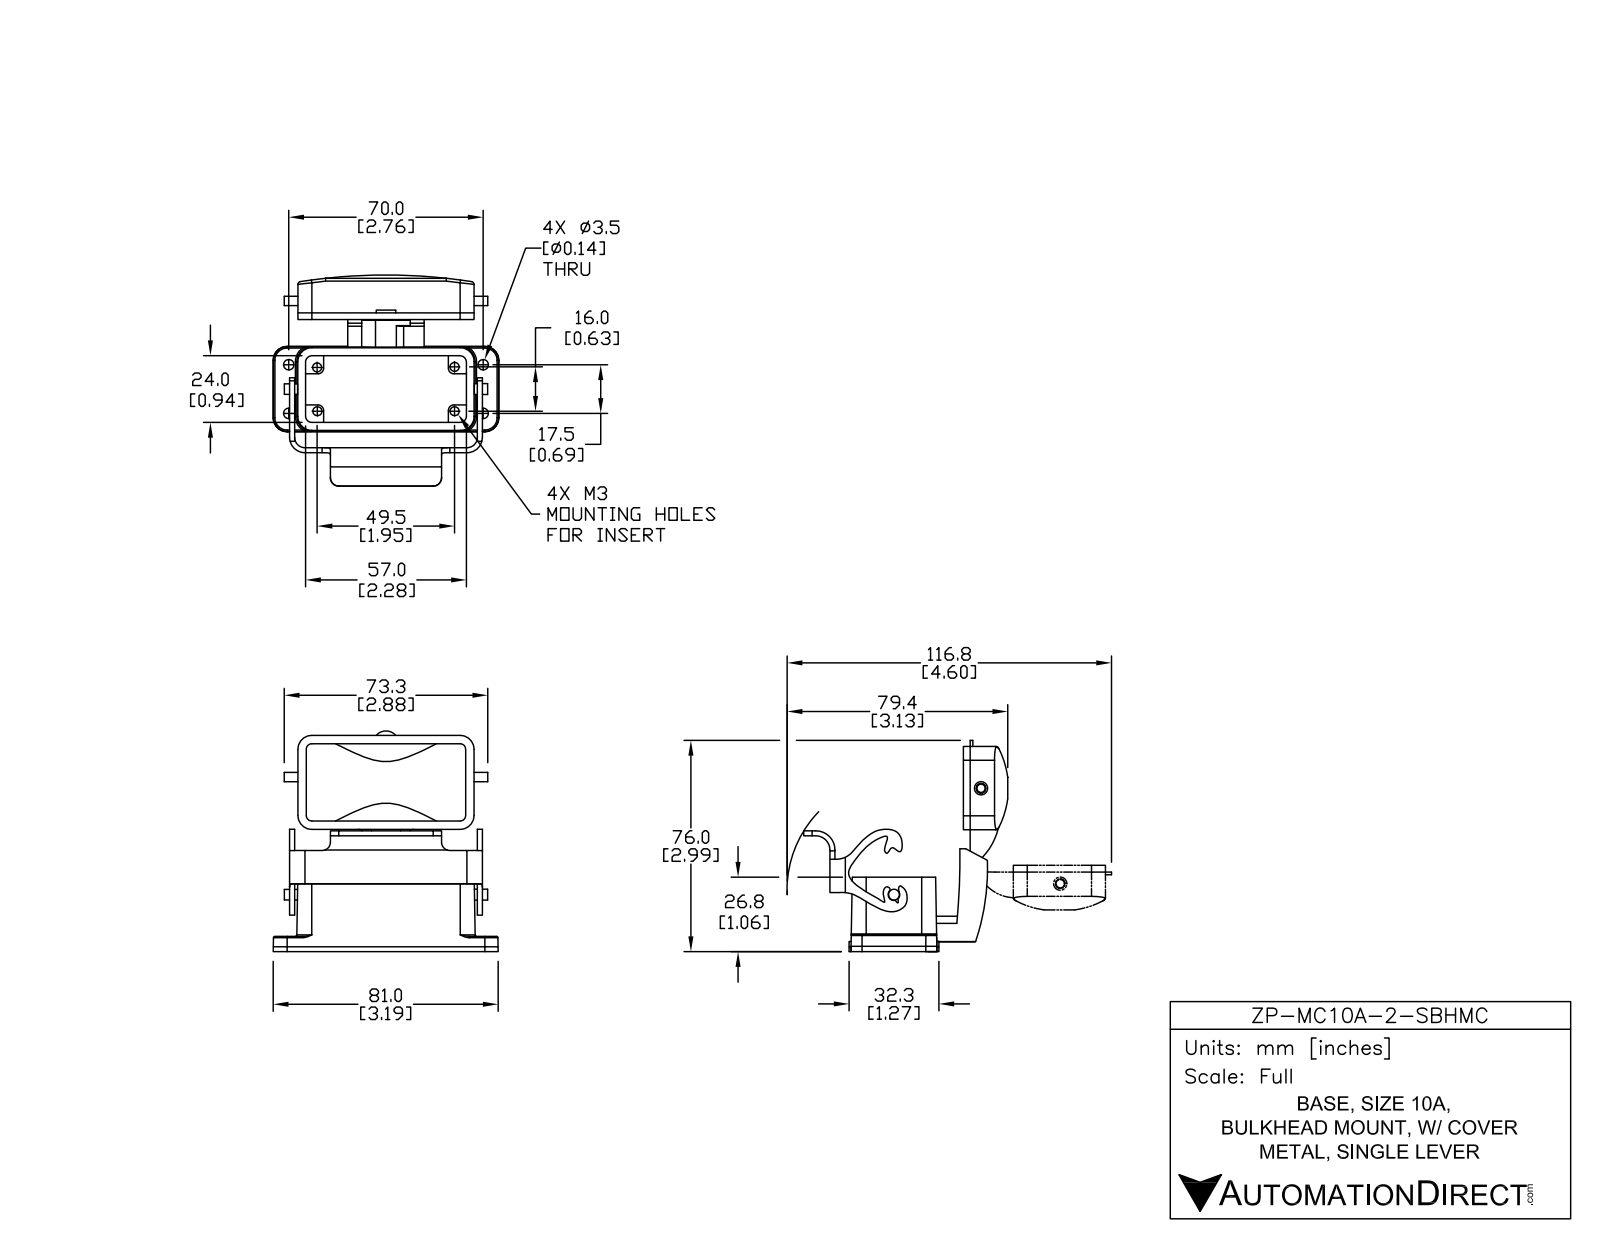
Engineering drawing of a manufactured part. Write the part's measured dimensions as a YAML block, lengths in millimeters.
part_name: "ZP-MC10A-2-SBHMC"
step_written_by: "SolidWorks 2014 (AUTOMOTIVE_DESIGN)"
units: millimeters
bodies: {solids: 3, faces: 295, planar: 130, cylindrical: 97, other: 68}
overall_size: [81.2, 75.98, 75.62]
volume: 40506
surface_area: 29630
round_holes:
  - {diameter: 3, count: 4}
  - {diameter: 3.5, count: 4}
round_bosses_or_shafts:
  - {diameter: 7.5, count: 1}
  - {diameter: 3.9, count: 1}
  - {diameter: 3.8, count: 1}
  - {diameter: 3.35, count: 1}
partial_cylinders:
  - {radius: 2, count: 10}
  - {radius: 0.5, count: 6}
  - {radius: 5, count: 6}
  - {radius: 1, count: 5}
  - {radius: 3, count: 4}
  - {radius: 3.75, count: 2}
  - {radius: 5.55, count: 2}
  - {radius: 2.1, count: 1}
face_to_face_distances: [3, 2.77, 27, 1.8, 2.78, 47, 44, 74, 63.4, 71]
hole_center_spacings: [10.28, 19.64, 59.75, 62.05, 16, 17.5, 49.5, 52.02]
